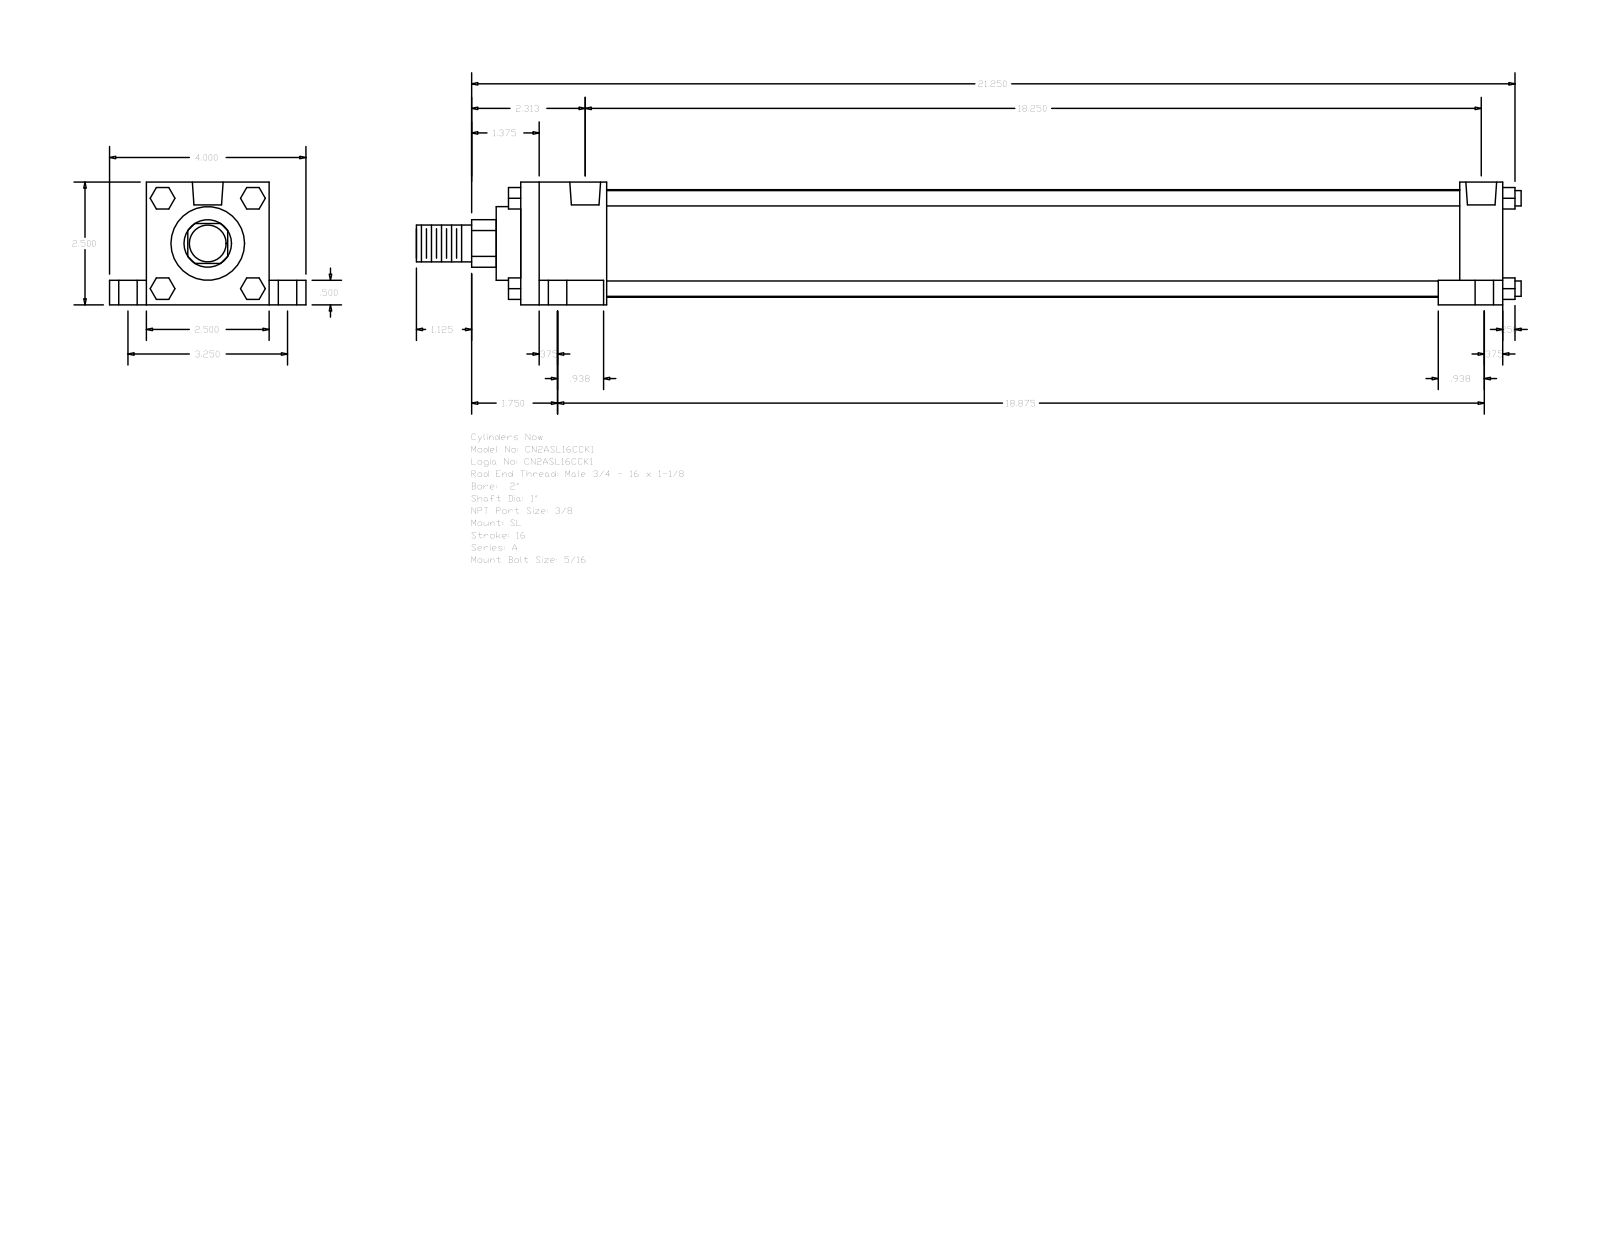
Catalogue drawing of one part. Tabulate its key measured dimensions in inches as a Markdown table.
| quantity | value |
| --- | --- |
| part name | A_SL__0200_1 |
| STEP written by | GSSL Pune (CONFIG_CONTROL_DESIGN) |
| units | inches |
| bodies | 0 solids, 148 faces (112 planar, 36 cylindrical, 0 other) |
| overall size | 22.5 × 4 × 2.5 |
| round holes (diameter × count) | 0.219 × 4, 0.375 × 4, 0.625 × 4, 0.627 × 2 |
| round bosses / shafts (diameter × count) | 0.313 × 4, 2.19 × 1, 1.5 × 1, 1 × 1, 0.75 × 1 |
| partial cylindrical surfaces (radius × count) | 0.484 × 1 |
| main face-to-face distances | 2.5, 20, 0.5, 2, 0.875, 0.75, 3.25, 1.75, 18.25, 19.125 |
| hole center spacings | 1.626, 1.639, 1.719, 1.741, 3.25, 18.031, 18.322, 18.385 |
